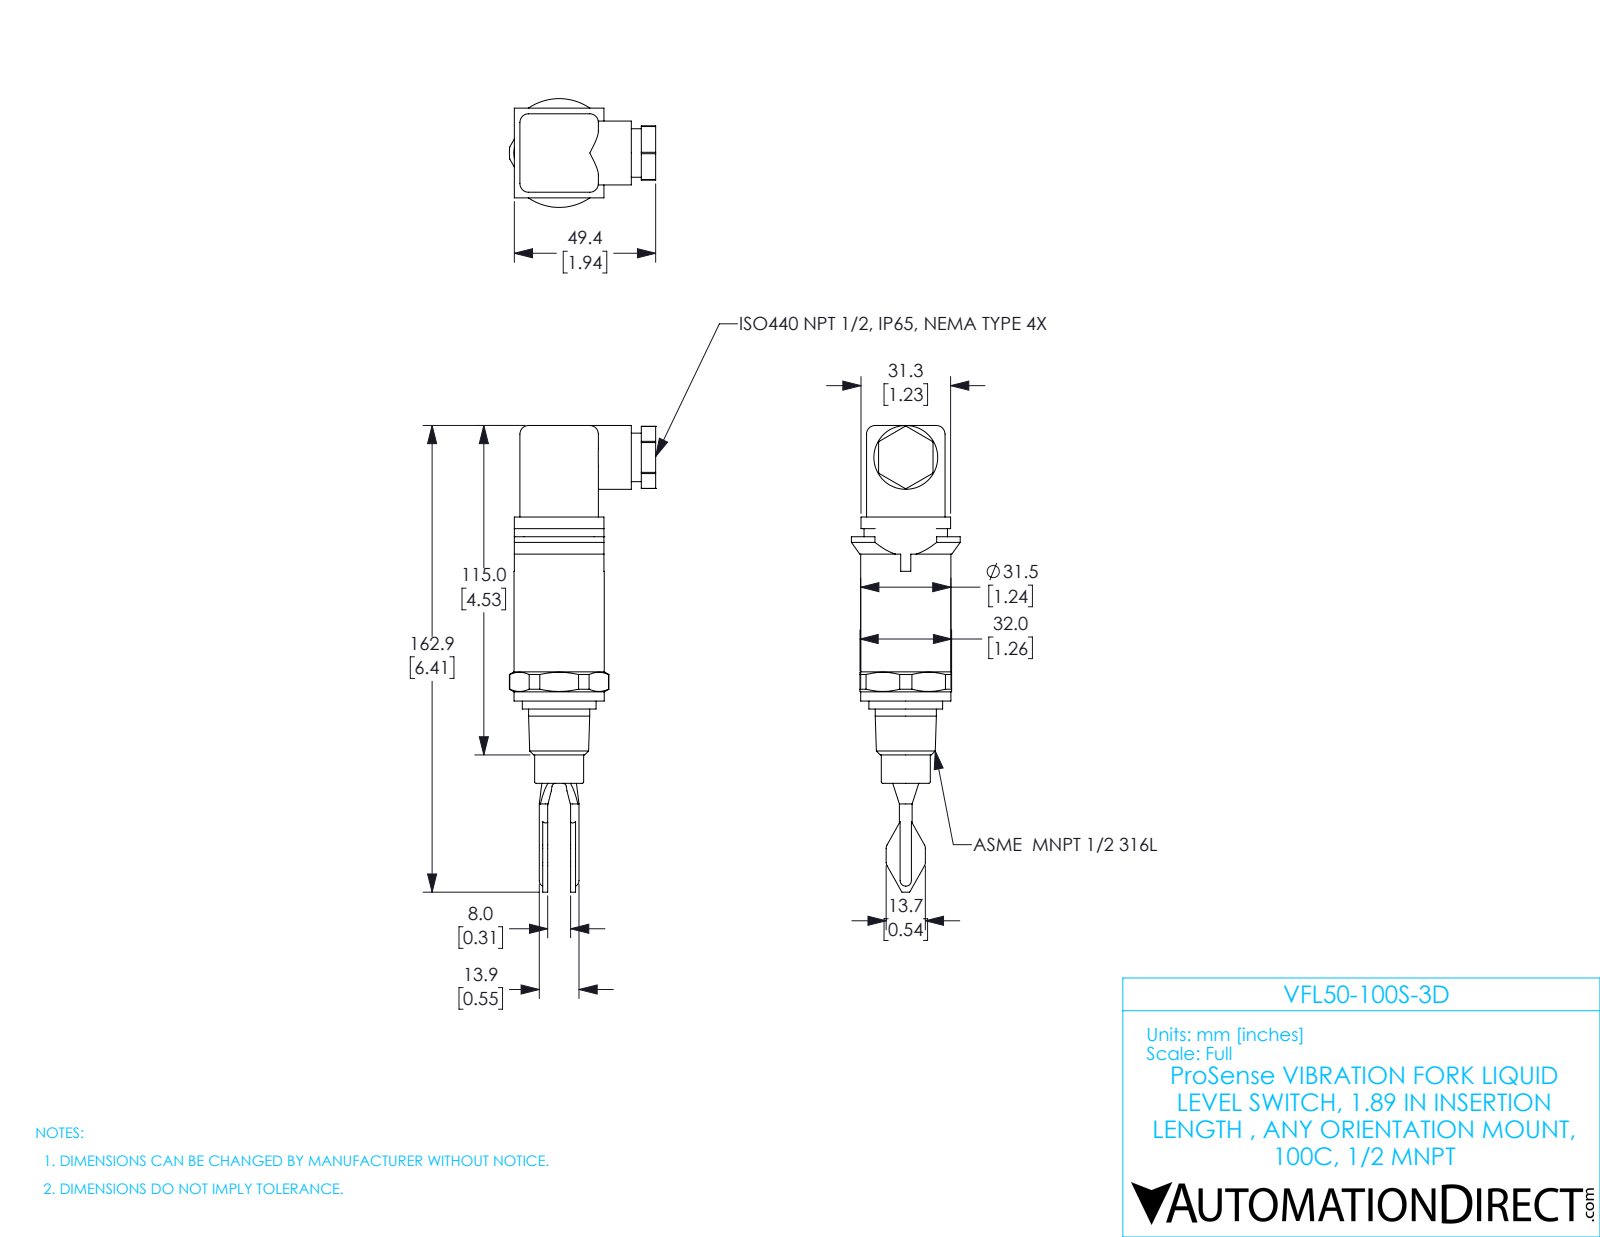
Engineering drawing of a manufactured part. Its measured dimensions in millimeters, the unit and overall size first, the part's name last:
Units: millimetres
Overall size (bounding box): 162.9 × 51.1 × 38
Round bosses / shafts (diameter × count): ⌀31.5 ×1, ⌀25.8 ×1, ⌀22.3 ×1, ⌀21.3 ×1, ⌀17.1 ×1, ⌀16.9 ×1
Partial cylindrical surfaces — rounded edges, fillets, slot ends (radius × count): R3 ×8, R1.2 ×4, R2.4 ×4, R3.9 ×4, R2.2 ×2, R10.8 ×1, R17.4 ×1, R19 ×1
Main face-to-face distances: 27.4, 2, 29.4, 11.7, 19.7, 9.7, 17.7, 31.3, 29.7, 49.4
Volume: 93 950 mm³ · Surface area: 16 850 mm²
Bodies: 1 solid, 158 faces (79 planar, 58 cylindrical, 21 other)
Part name (STEP PRODUCT): VFL50-100S-3D
STEP written by: SolidWorks 2017 (AUTOMOTIVE_DESIGN)
